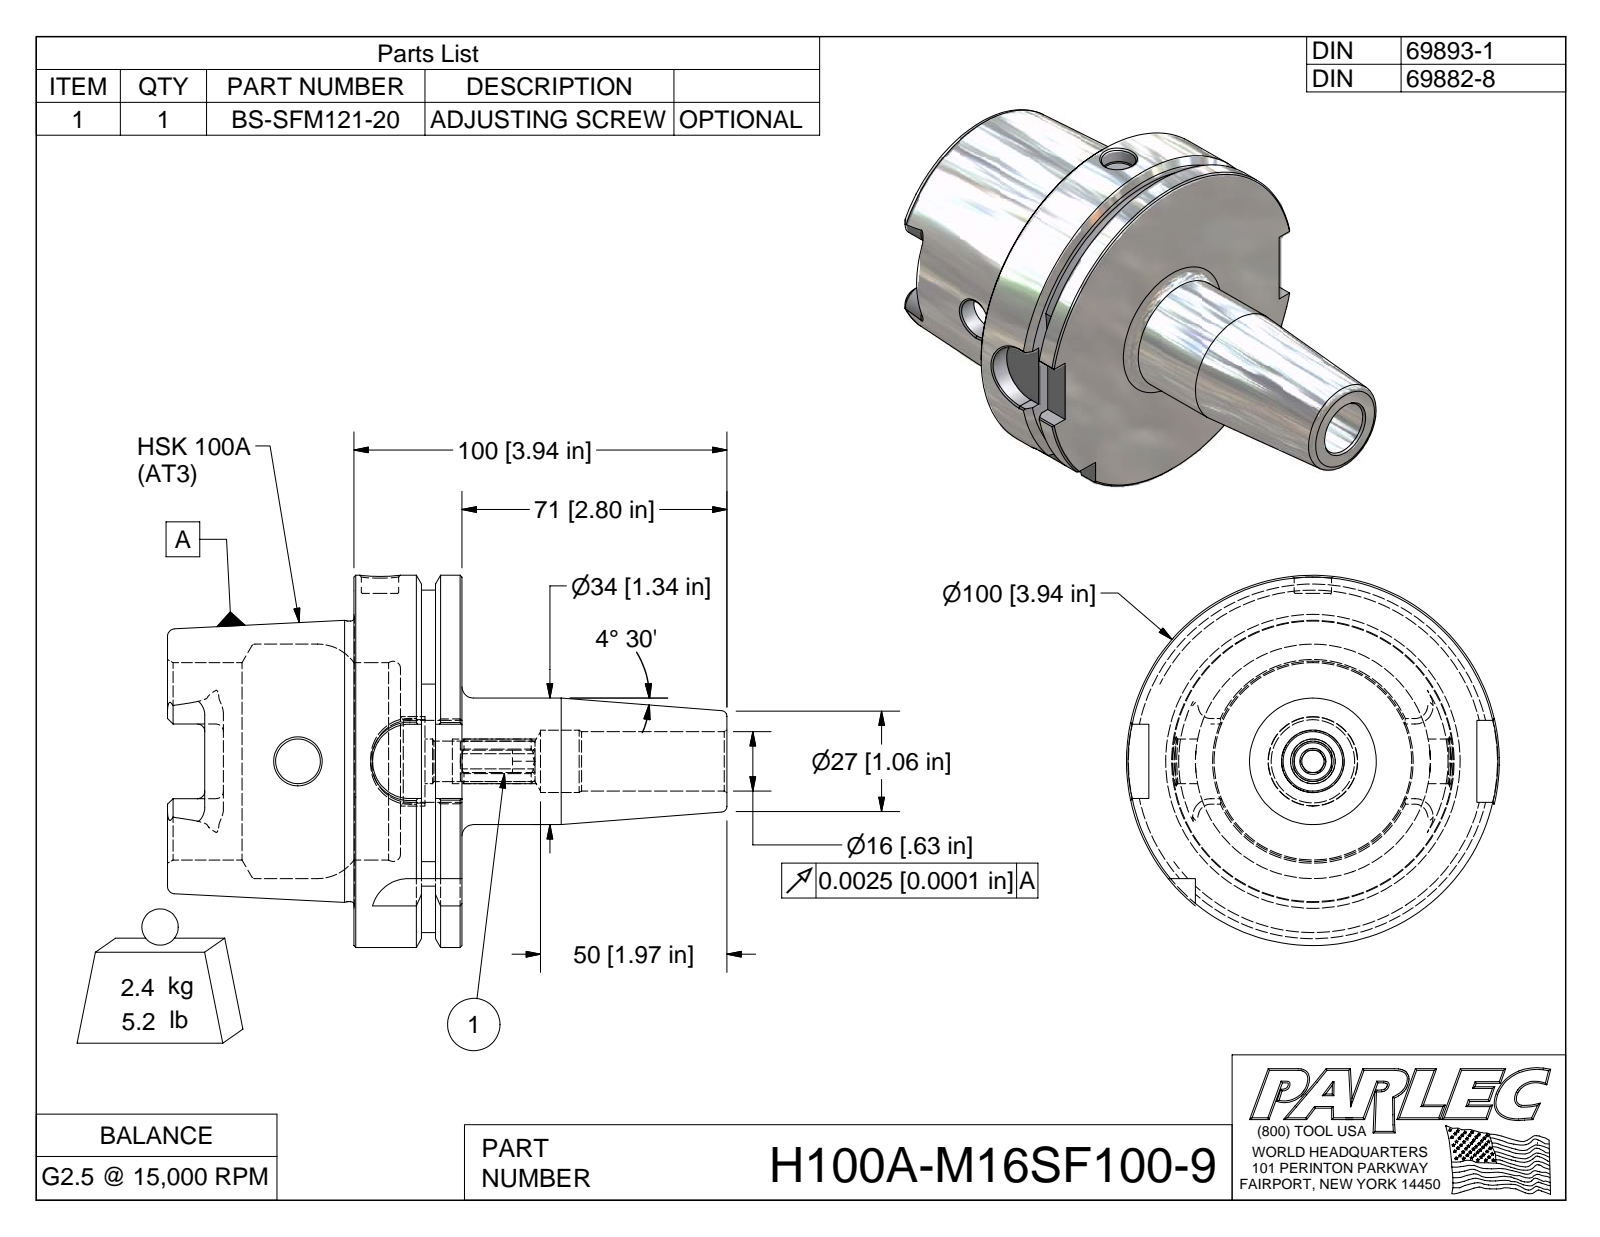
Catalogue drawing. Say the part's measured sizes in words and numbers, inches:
The part is named "H100A-M16SF100-9; H100A-M16SF100-9-1; BS-SFM121-20". Its 3-D file was written by "Autodesk Inventor 2009 (AUTOMOTIVE_DESIGN)". It is 2 solids with 147 faces: 48 planar, 29 cylindrical and 70 other. Overall it measures 5.909 by 3.937 by 3.937 inches. Its volume is 18.49 cubic inches and its surface area 93.64 square inches. Round holes: 1 of diameter 0.394, 1 of diameter 0.472, 1 of diameter 0.629, 1 of diameter 0.659, 1 of diameter 0.881, 1 of diameter 2.087, 1 of diameter 2.48. Round bosses or shafts: 1 of diameter 3.937, 1 of diameter 2.967, 1 of diameter 1.339. Partial cylindrical surfaces (rounded edges, fillets, slot ends): 4 of radius 0.394, 3 of radius 0.079, 2 of radius 0.192, 1 of radius 0.236, 1 of radius 1.811. The main face-to-face distances are 1.142, 0.492, 0.65, 1.969, 2.461, 3.11, 2.682, 0.713, 0.221, 0.428.
